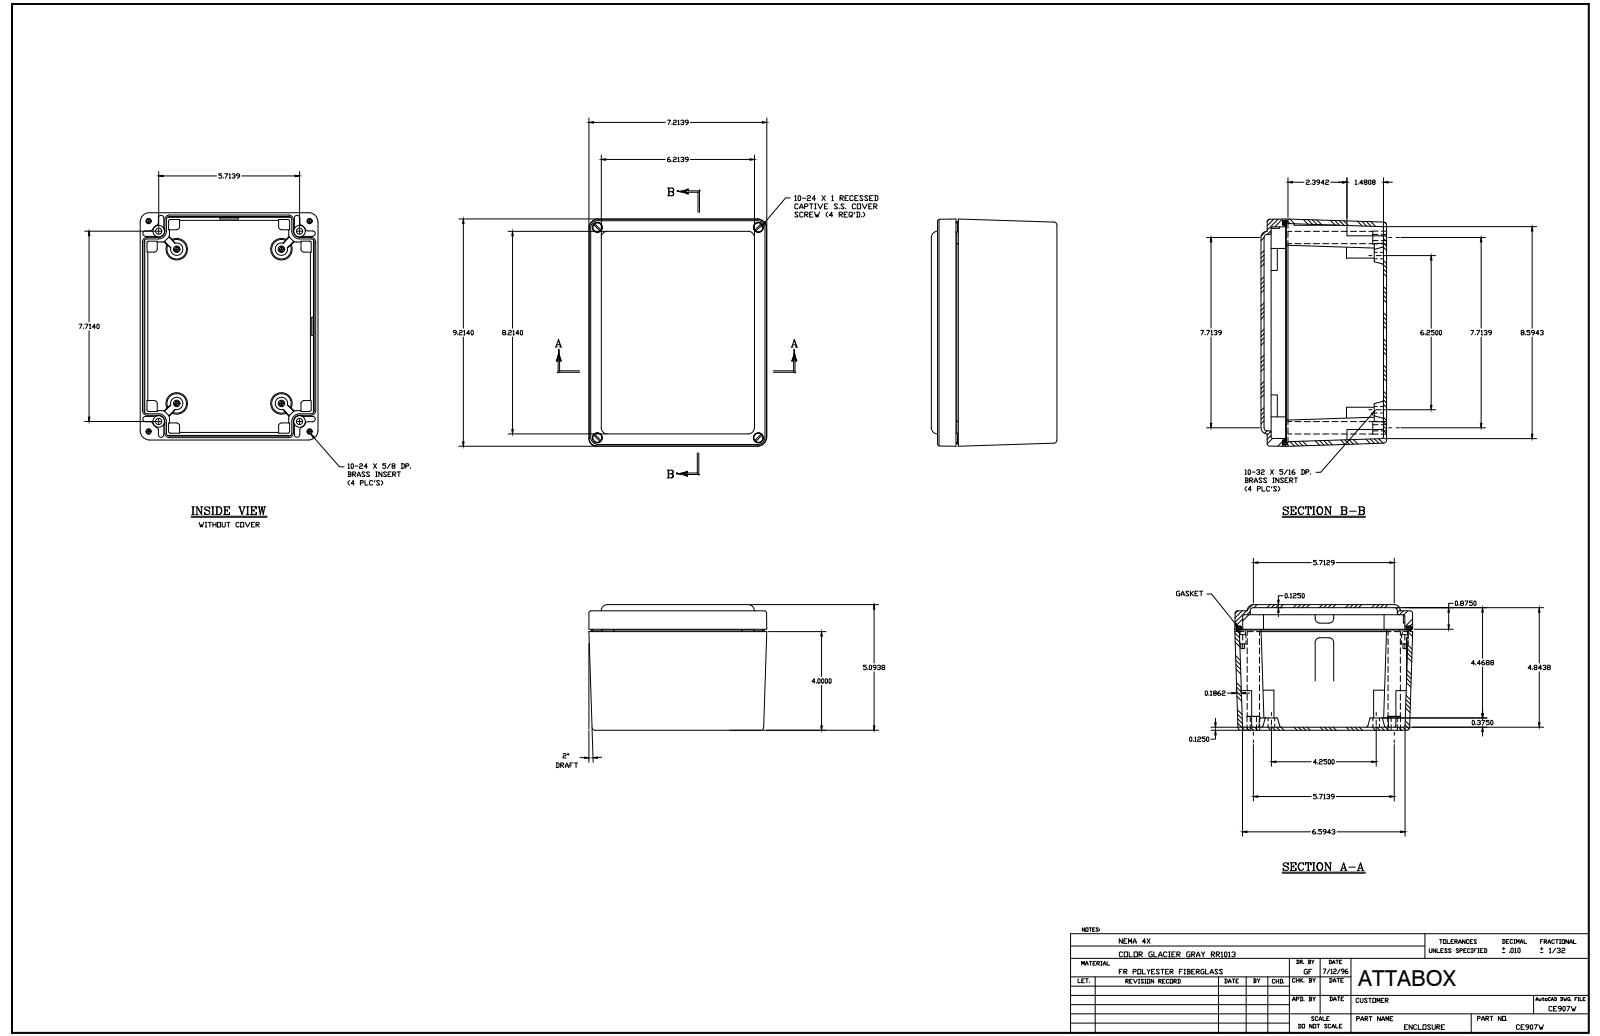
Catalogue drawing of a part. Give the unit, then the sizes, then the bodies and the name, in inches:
Units: inches
Overall size (bounding box): 9.22 × 7.22 × 5.094
Round holes (diameter × count): ⌀0.281 ×8, ⌀0.145 ×4, ⌀0.156 ×4, ⌀0.156 ×4, ⌀0.19 ×4, ⌀0.219 ×4, ⌀0.23 ×4, ⌀0.28 ×4, ⌀0.313 ×4, ⌀0.406 ×4, ⌀0.531 ×4
Round bosses / shafts (diameter × count): ⌀0.375 ×4, ⌀0.364 ×4, ⌀0.191 ×4
Partial cylindrical surfaces — rounded edges, fillets, slot ends (radius × count): R0.031 ×57, R0.125 ×38, R0.063 ×24, R0.01 ×16, R0.059 ×8, R0.062 ×8, R0.188 ×8, R0.25 ×8
Main face-to-face distances: 0.186, 0.125, 4.844, 5.094, 4.969, 0.125, 4.969, 4.094, 0.75, 0.25
Hole centre spacings: 0.574, 0.574, 1.039, 1.613, 1.613, 5.04, 5.511, 5.511
Volume: 57.17 in³ · Surface area: 648 in²
Bodies: 23 solids, 1100 faces (436 planar, 296 cylindrical, 368 other)
Part name (STEP PRODUCT): CE907W
STEP written by: SolidWorks 2018 (AUTOMOTIVE_DESIGN)
